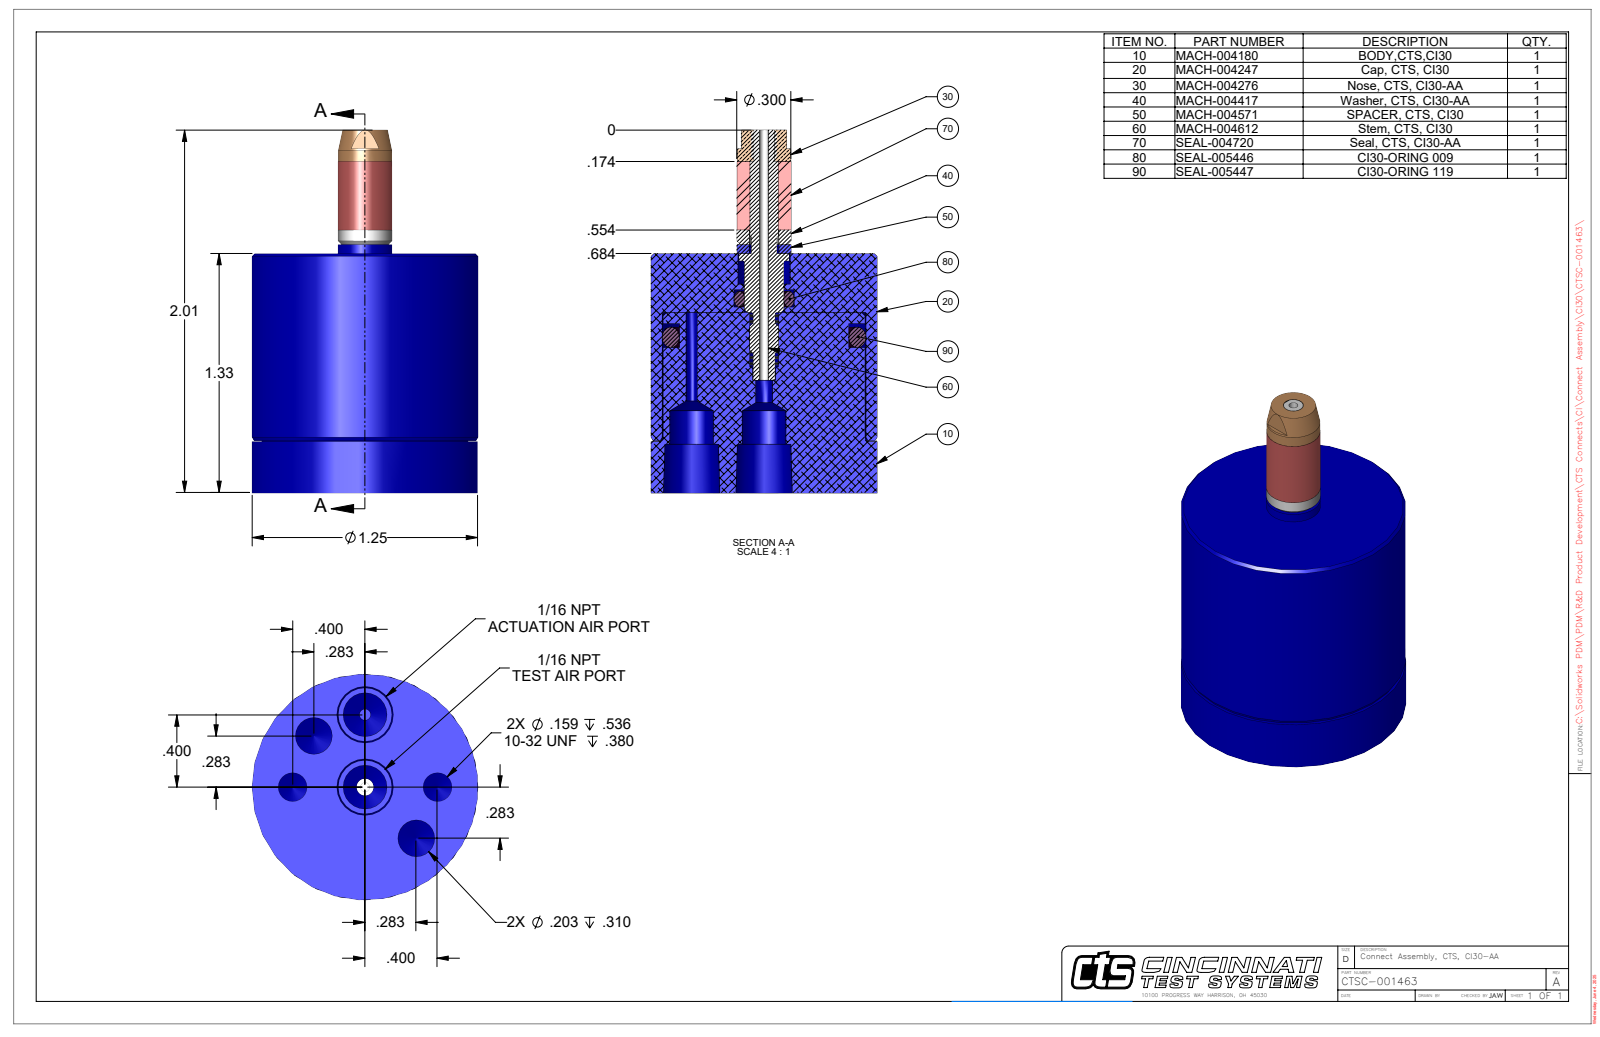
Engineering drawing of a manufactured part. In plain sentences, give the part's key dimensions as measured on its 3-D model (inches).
The part is named "CTSC-001463". Its 3-D file was written by "SolidWorks 2023 (AUTOMOTIVE_DESIGN)". It is 1 solid with 82 faces: 18 planar, 36 cylindrical and 28 other. Overall it measures 2.009 by 1.25 by 1.25 inches. Its volume is 1.559 cubic inches and its surface area 13.08 square inches. Round holes: 2 of diameter 0.159, 2 of diameter 0.203, 2 of diameter 0.242, 1 of diameter 0.052, 1 of diameter 0.062, 1 of diameter 0.094, 1 of diameter 0.289, 1 of diameter 1.125. Round bosses or shafts: 1 of diameter 1.25, 1 of diameter 1.115, 1 of diameter 0.3, 1 of diameter 0.297, 1 of diameter 0.277. The main face-to-face distances are 1.325, 0.287, 1.039, 0.29, 1.035, 2.009, 1.722, 1.719, 0.684, 0.271. The hole center spacings are 0.306, 0.4, 0.739, 0.4, 0.566, 0.8, 0.8.
